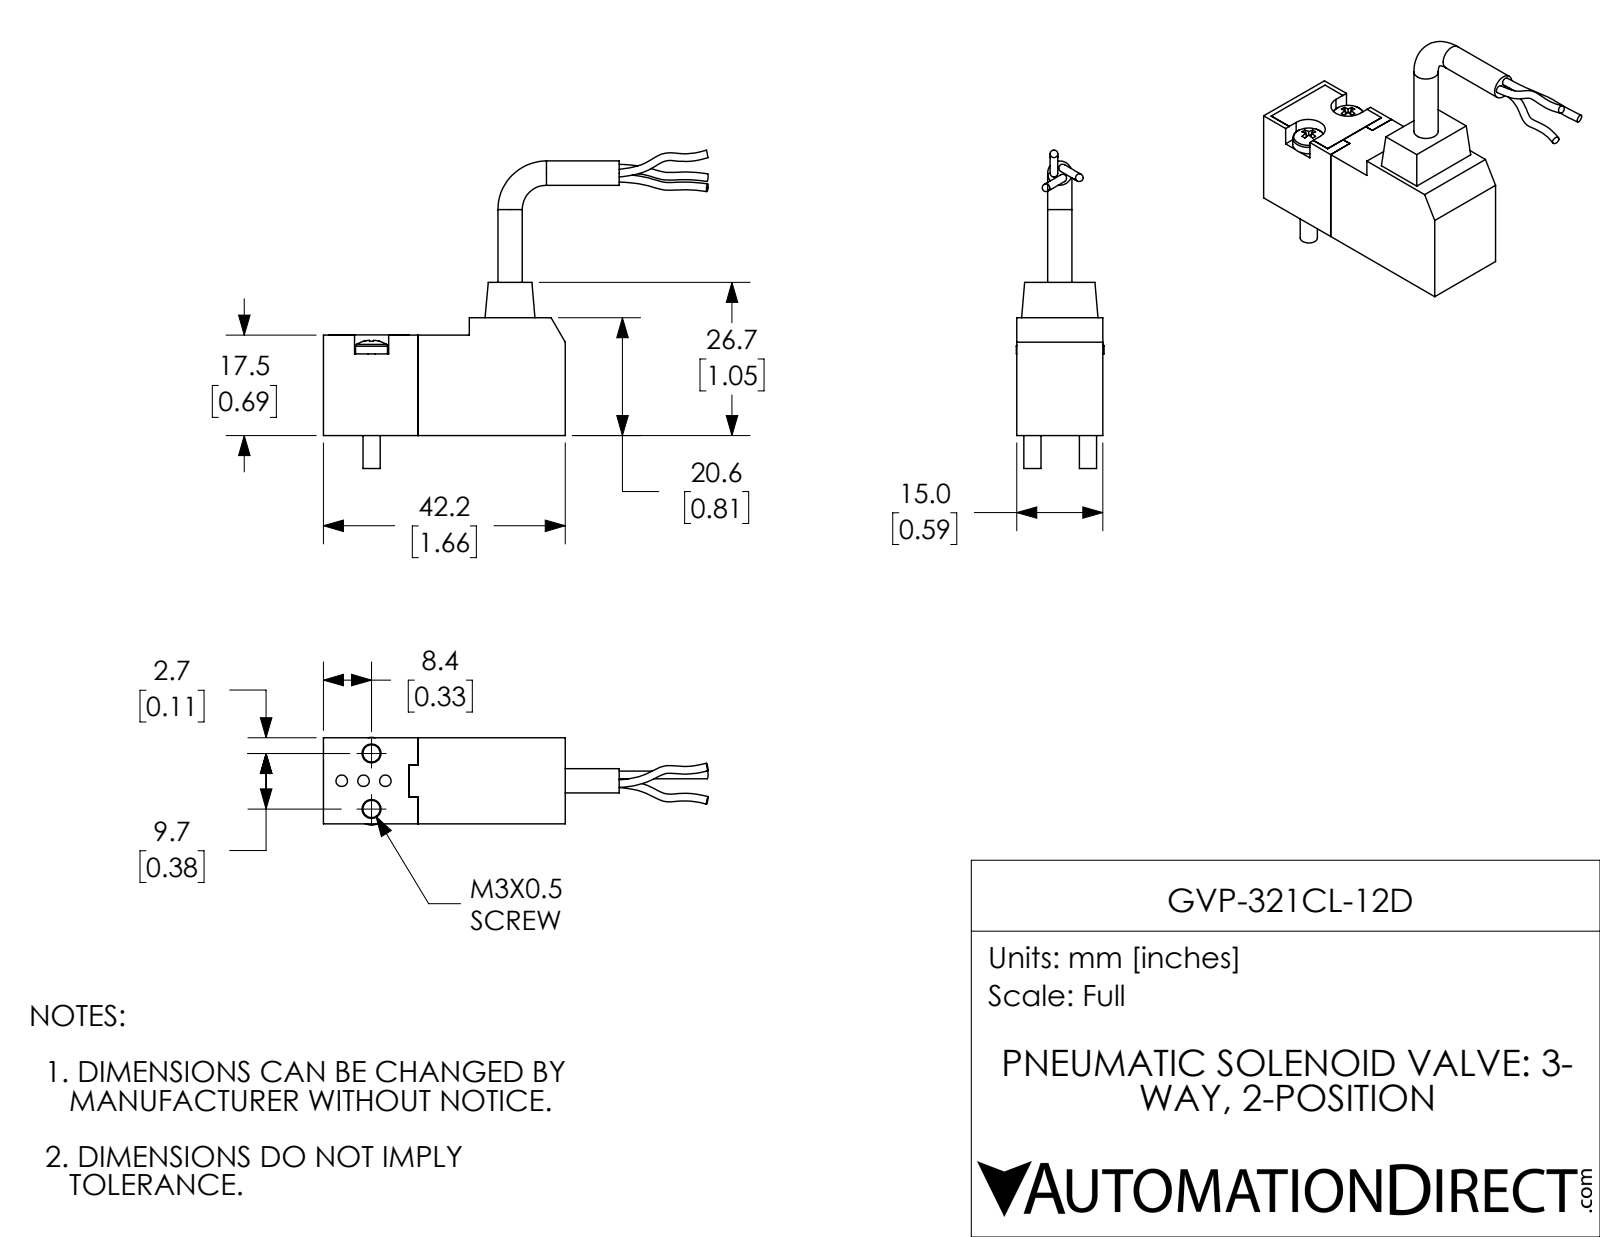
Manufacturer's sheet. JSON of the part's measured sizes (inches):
{"part_name": "GVP-321CL-12D", "step_written_by": "SolidWorks 2018 (AUTOMOTIVE_DESIGN)", "units": "inches", "bodies": {"solids": 4, "faces": 120, "planar": 79, "cylindrical": 25, "other": 16}, "overall_size": [2.645, 2.188, 0.602], "volume_in3": 0.787, "surface_area_in2": 9.252, "round_holes": [[0.079, 3], [0.13, 2]], "round_bosses_or_shafts": [[0.22, 2], [0.167, 2], [0.118, 2]], "partial_cylinders_radius": [[0.117, 2]], "face_to_face_distances": [0.591, 0.651, 1.012, 1.663, 1.075, 0.063, 0.588, 0.69, 0.691, 0.185], "hole_center_spacings": [0.15, 0.196, 0.202, 0.21, 0.216, 0.278, 0.282, 0.3]}
